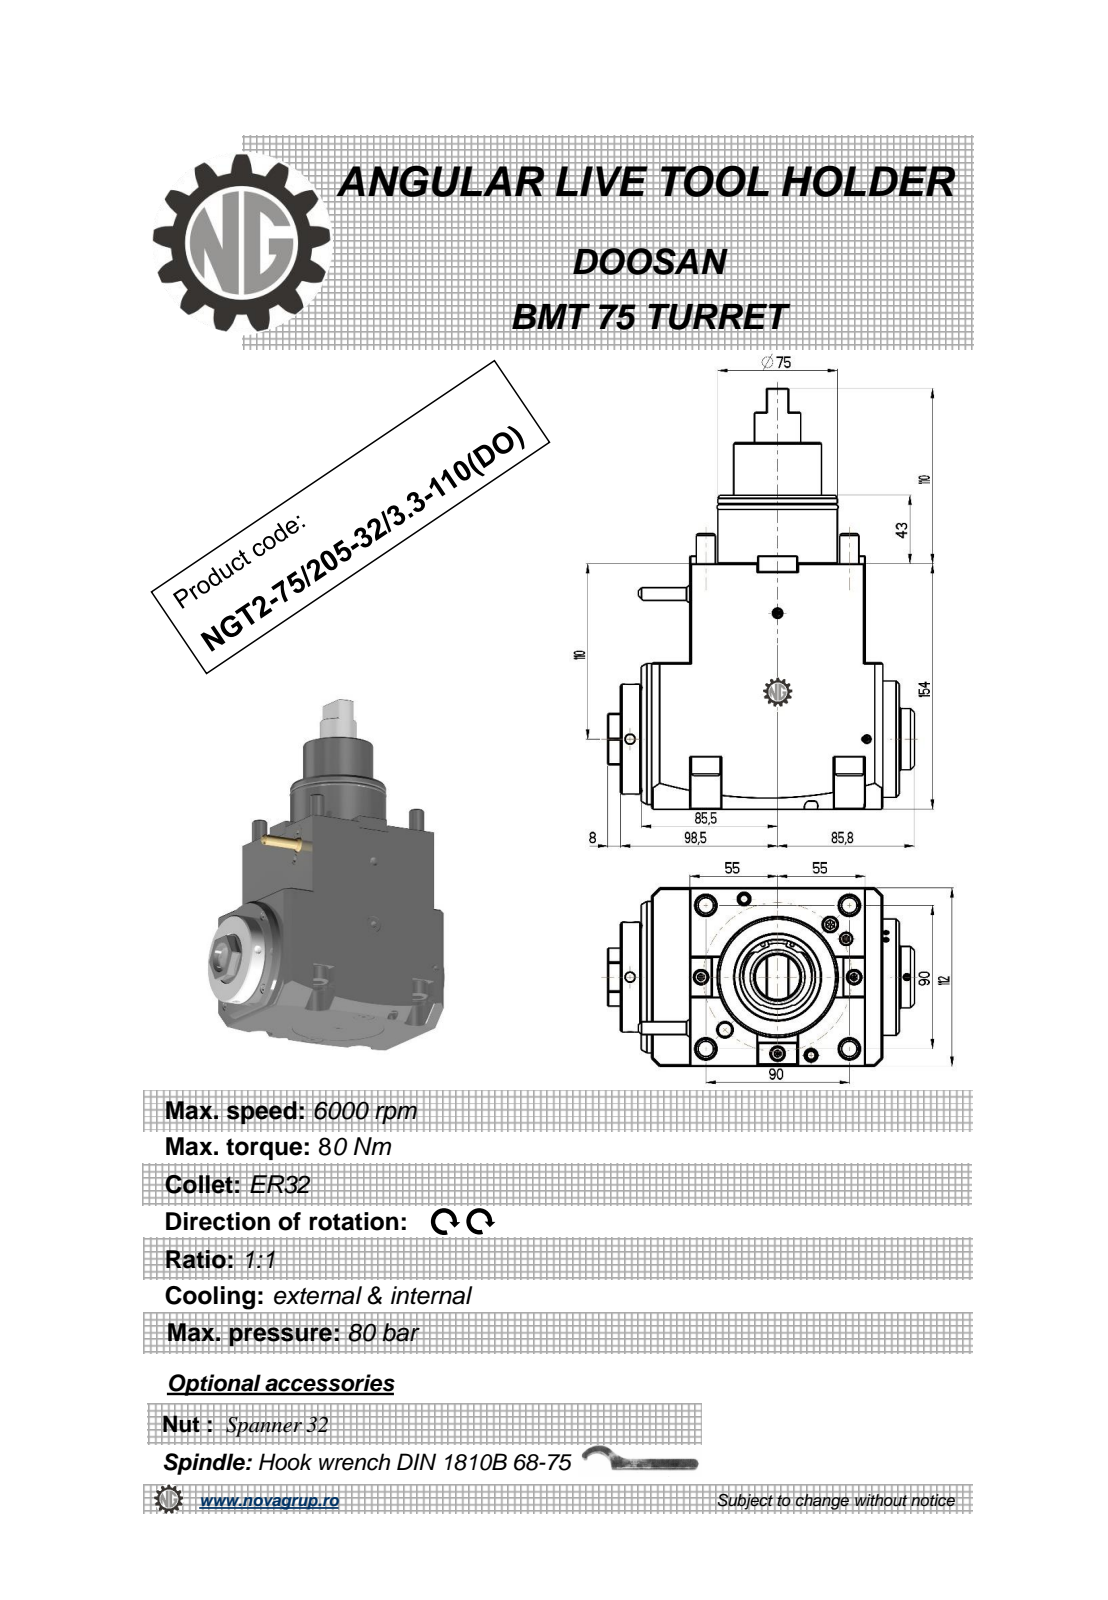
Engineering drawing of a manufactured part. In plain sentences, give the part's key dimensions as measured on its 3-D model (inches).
The part is named "NGT2_75_205_32_3_3_110_DO". Its 3-D file was written by "PRO/ENGINEER BY PARAMETRIC TECHNOLOGY CORPORATION, 2010280 (CONFIG_CONTROL_DESIGN)". It is 2 solids with 299 faces: 147 planar, 71 cylindrical and 81 other. Overall it measures 10.394 by 7.571 by 4.409 inches. Its volume is 162 cubic inches and its surface area 231.3 square inches. Round holes: 2 of diameter 0.236, 2 of diameter 0.335, 1 of diameter 0.118, 1 of diameter 0.197, 1 of diameter 0.906. Round bosses or shafts: 4 of diameter 0.709, 4 of diameter 0.472, 1 of diameter 3.74, 1 of diameter 2.953, 1 of diameter 2.913, 1 of diameter 2.874, 1 of diameter 2.756, 1 of diameter 2.717. Partial cylindrical surfaces (rounded edges, fillets, slot ends): 4 of radius 0.374, 2 of radius 0.031, 2 of radius 13.78. The main face-to-face distances are 4.409, 4.331, 6.063, 4.764, 0.433, 2.441, 1.713, 3.622, 1.201, 5.531. The hole center spacings are 2.679, 3.675, 3.798, 5.109.
